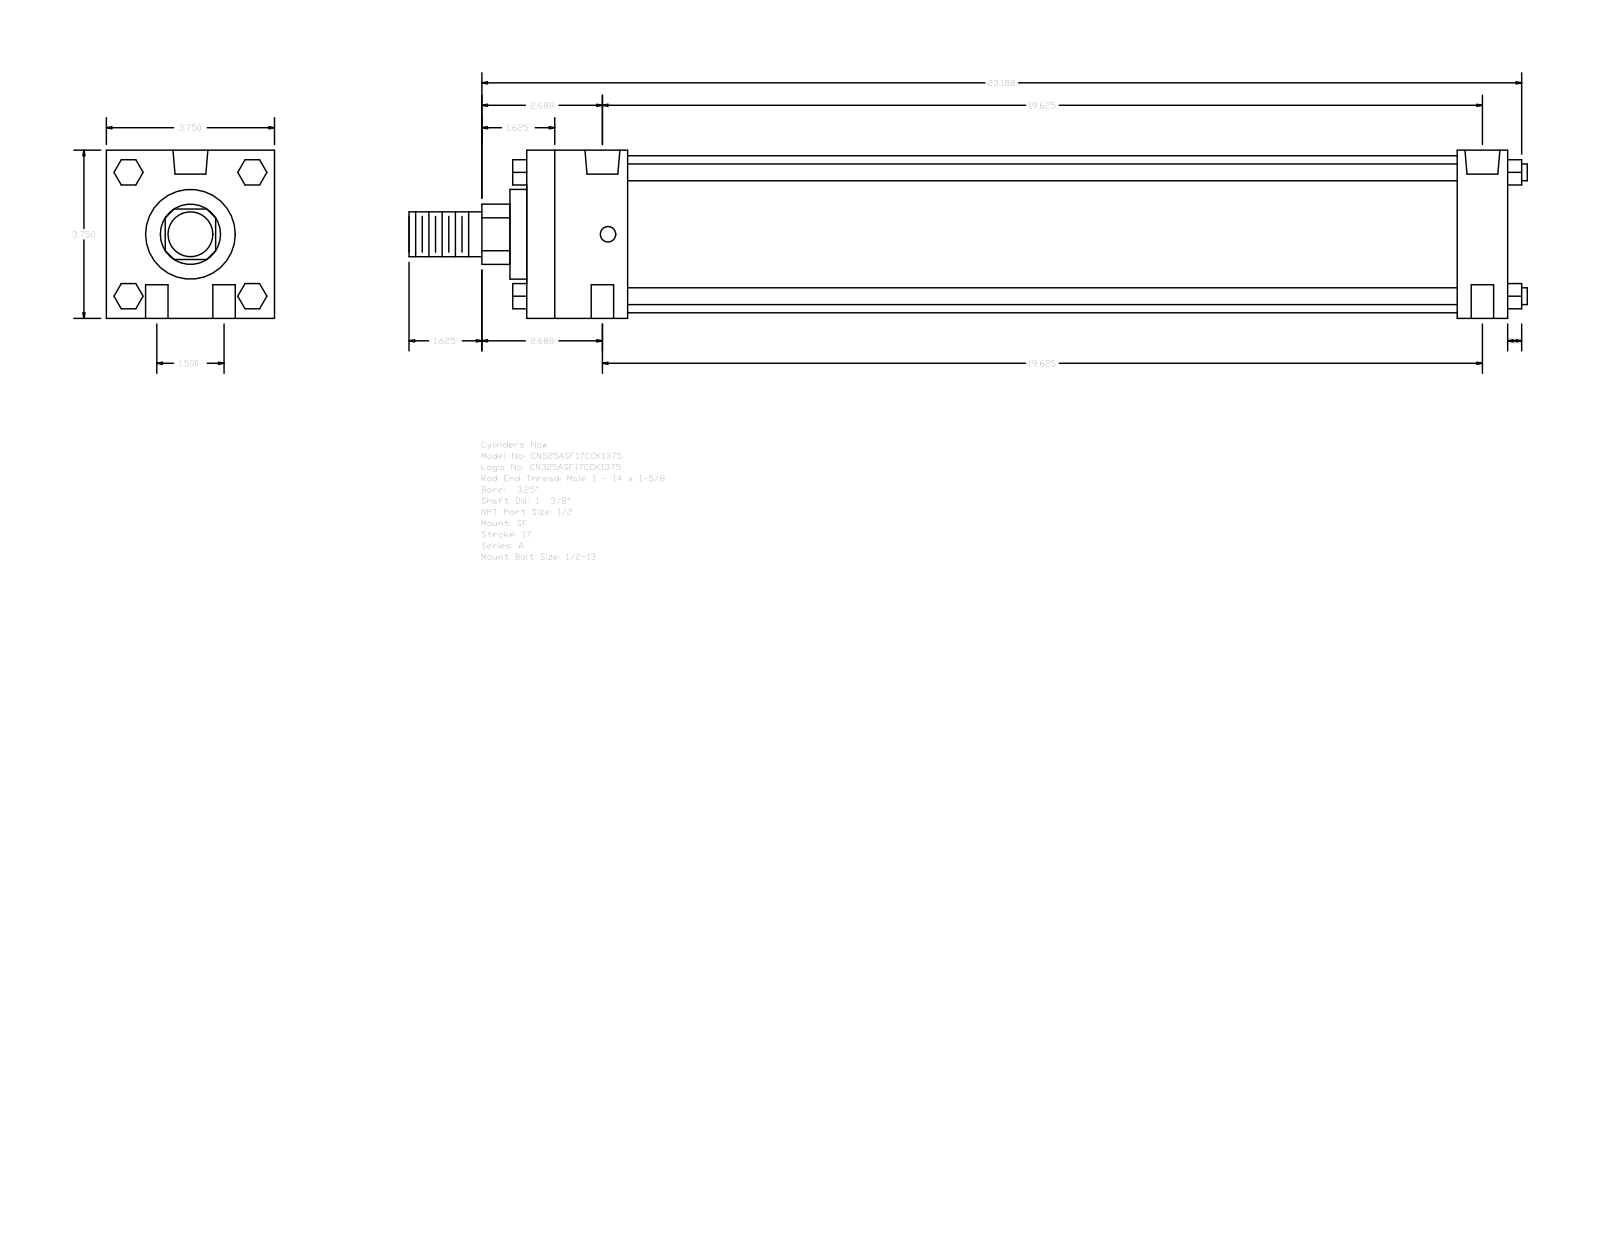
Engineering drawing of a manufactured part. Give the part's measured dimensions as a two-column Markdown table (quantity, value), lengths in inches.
| quantity | value |
| --- | --- |
| part name | A_SF__0325_1.375 |
| STEP written by | GSSL Pune (CONFIG_CONTROL_DESIGN) |
| units | inches |
| bodies | 0 solids, 124 faces (94 planar, 30 cylindrical, 0 other) |
| overall size | 24.937 × 3.75 × 3.75 |
| round holes (diameter × count) | 0.5 × 4, 0.344 × 2, 0.778 × 2 |
| round bosses / shafts (diameter × count) | 0.375 × 4, 3.5 × 1, 2 × 1, 1.375 × 1, 1 × 1 |
| partial cylindrical surfaces (radius × count) | 0.672 × 1 |
| main face-to-face distances | 3.75, 21.875, 2.25, 20.75, 1.125, 18.5, 19.625, 2.625, 0.375, 21.125 |
| hole center spacings | 0.75, 19.639, 19.625, 1.5, 19.682, 19.375 |
